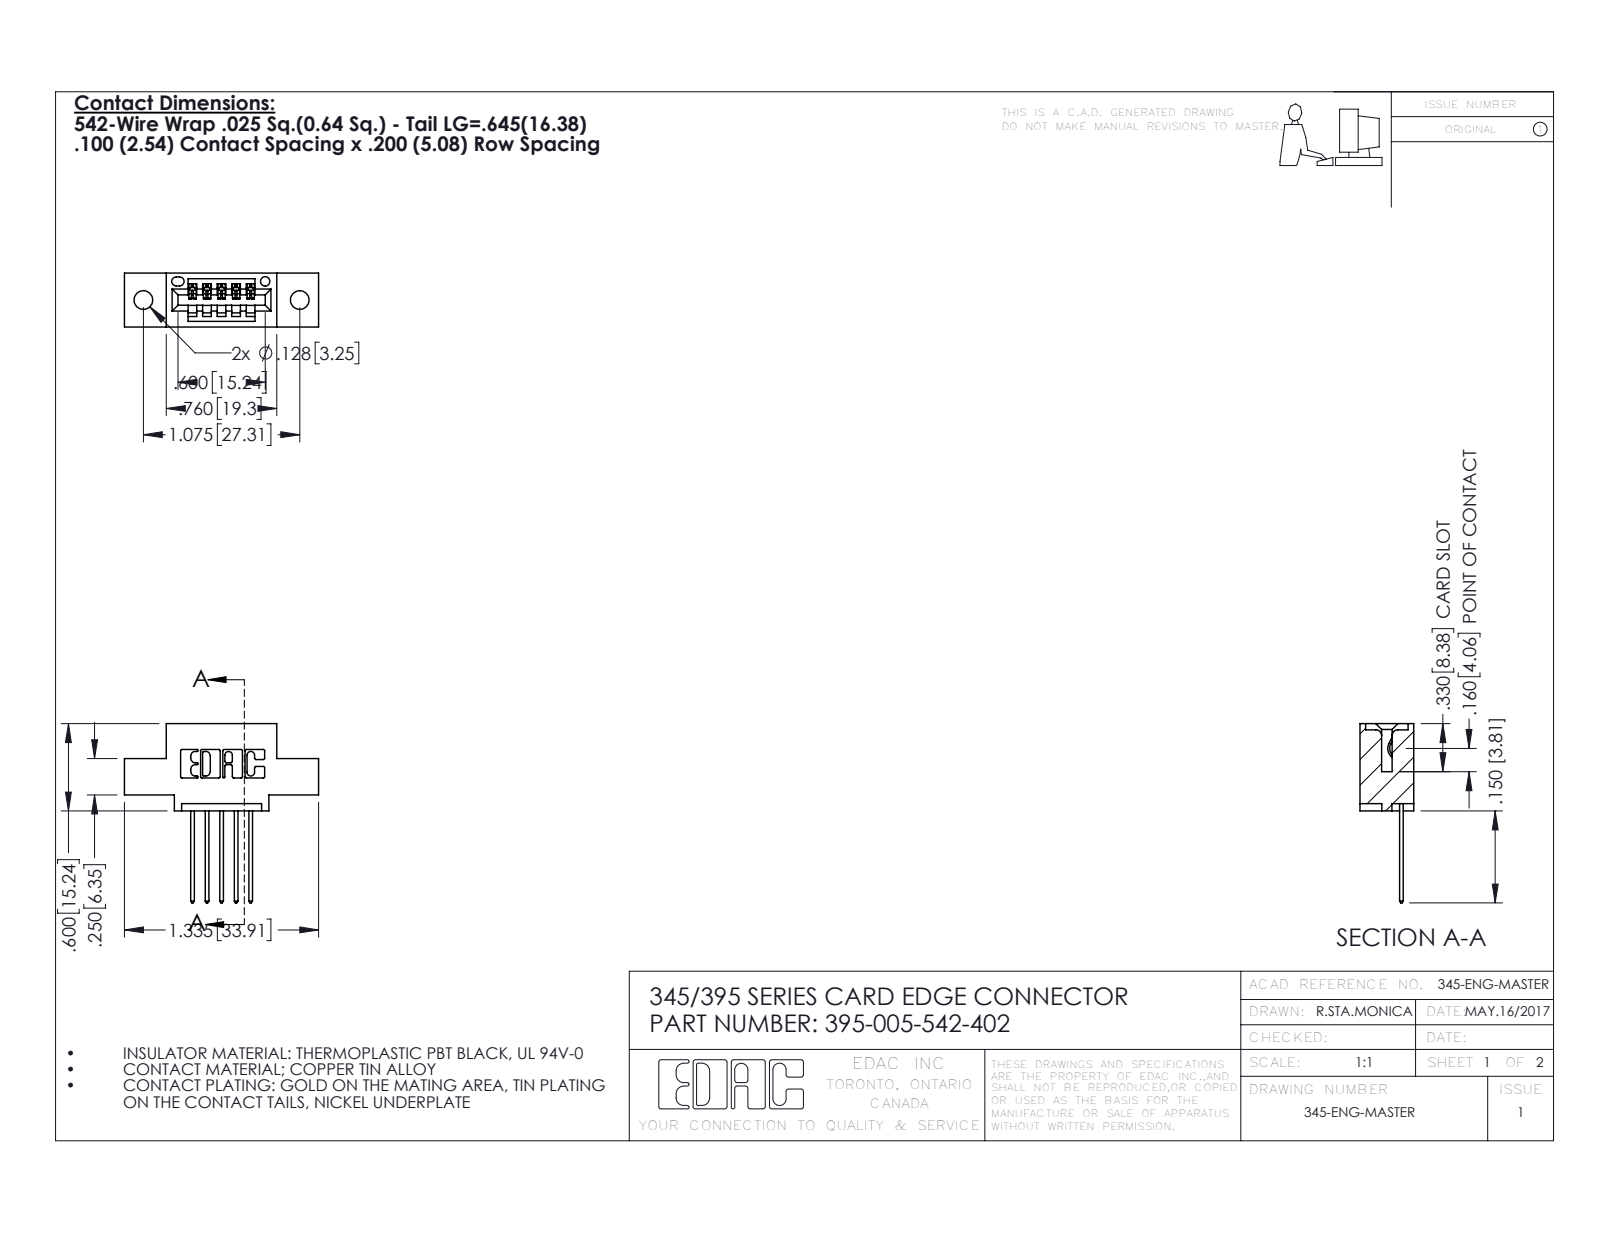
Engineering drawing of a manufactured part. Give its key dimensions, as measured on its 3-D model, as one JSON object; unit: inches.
{"part_name": "345-292-001_345-293-142; 345 Part_0.110 Offset - 0.128 Dia; 395-005-542-402", "step_written_by": "SolidWorks 2016 (CONFIG_CONTROL_DESIGN)", "units": "inches", "bodies": {"solids": 6, "faces": 420, "planar": 284, "cylindrical": 136, "other": 0}, "overall_size": [1.335, 1.232, 0.37], "volume_in3": 0.172, "surface_area_in2": 4.842, "round_holes": [[0.128, 2], [0.064, 1]], "partial_cylinders_radius": [[0.01, 22], [0.006, 10], [0.01, 10], [0.007, 6], [0.031, 6], [0.026, 3], [0.031, 2], [0.04, 2]], "face_to_face_distances": [0.2, 0.37, 0.298, 0.072, 0.1, 0.025, 0.098, 0.272, 0.25, 0.06], "hole_center_spacings": [0.27, 0.847, 1.075]}
